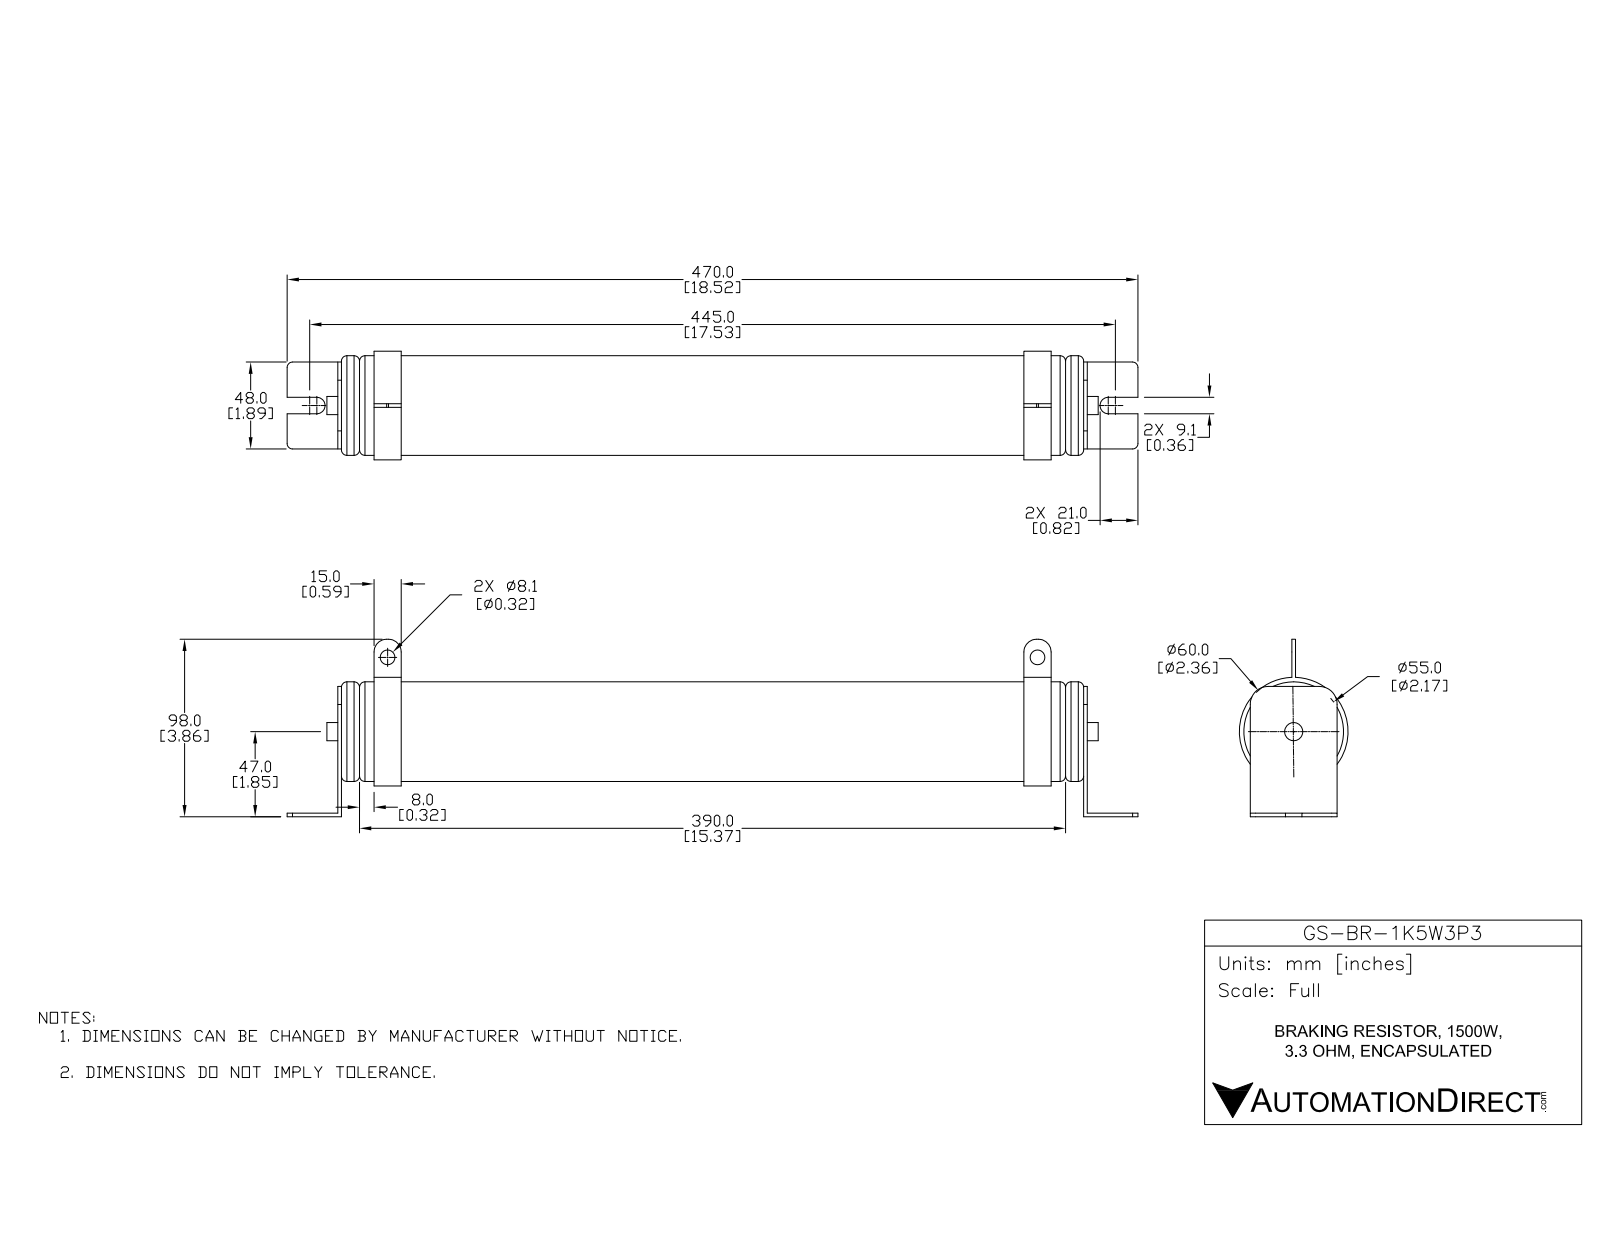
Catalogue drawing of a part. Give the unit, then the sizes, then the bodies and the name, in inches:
Units: inches
Overall size (bounding box): 18.504 × 3.858 × 2.362
Round holes (diameter × count): ⌀0.319 ×2
Round bosses / shafts (diameter × count): ⌀2.362 ×1, ⌀2.166 ×1, ⌀2.165 ×1, ⌀0.394 ×1
Partial cylindrical surfaces — rounded edges, fillets, slot ends (radius × count): R0.118 ×4, R0.276 ×4, R0.179 ×2, R0.394 ×2
Main face-to-face distances: 0.079, 16.299, 16.22, 16.142, 1.378, 14.921, 1.299, 14.843, 0.787, 15.512
Hole centre spacings: 14.134
Volume: 61.39 in³ · Surface area: 143.2 in²
Bodies: 2 solids, 91 faces (41 planar, 38 cylindrical, 12 other)
Part name (STEP PRODUCT): GS-BR-1K5W3P3
STEP written by: SolidWorks 2015 (AUTOMOTIVE_DESIGN)
